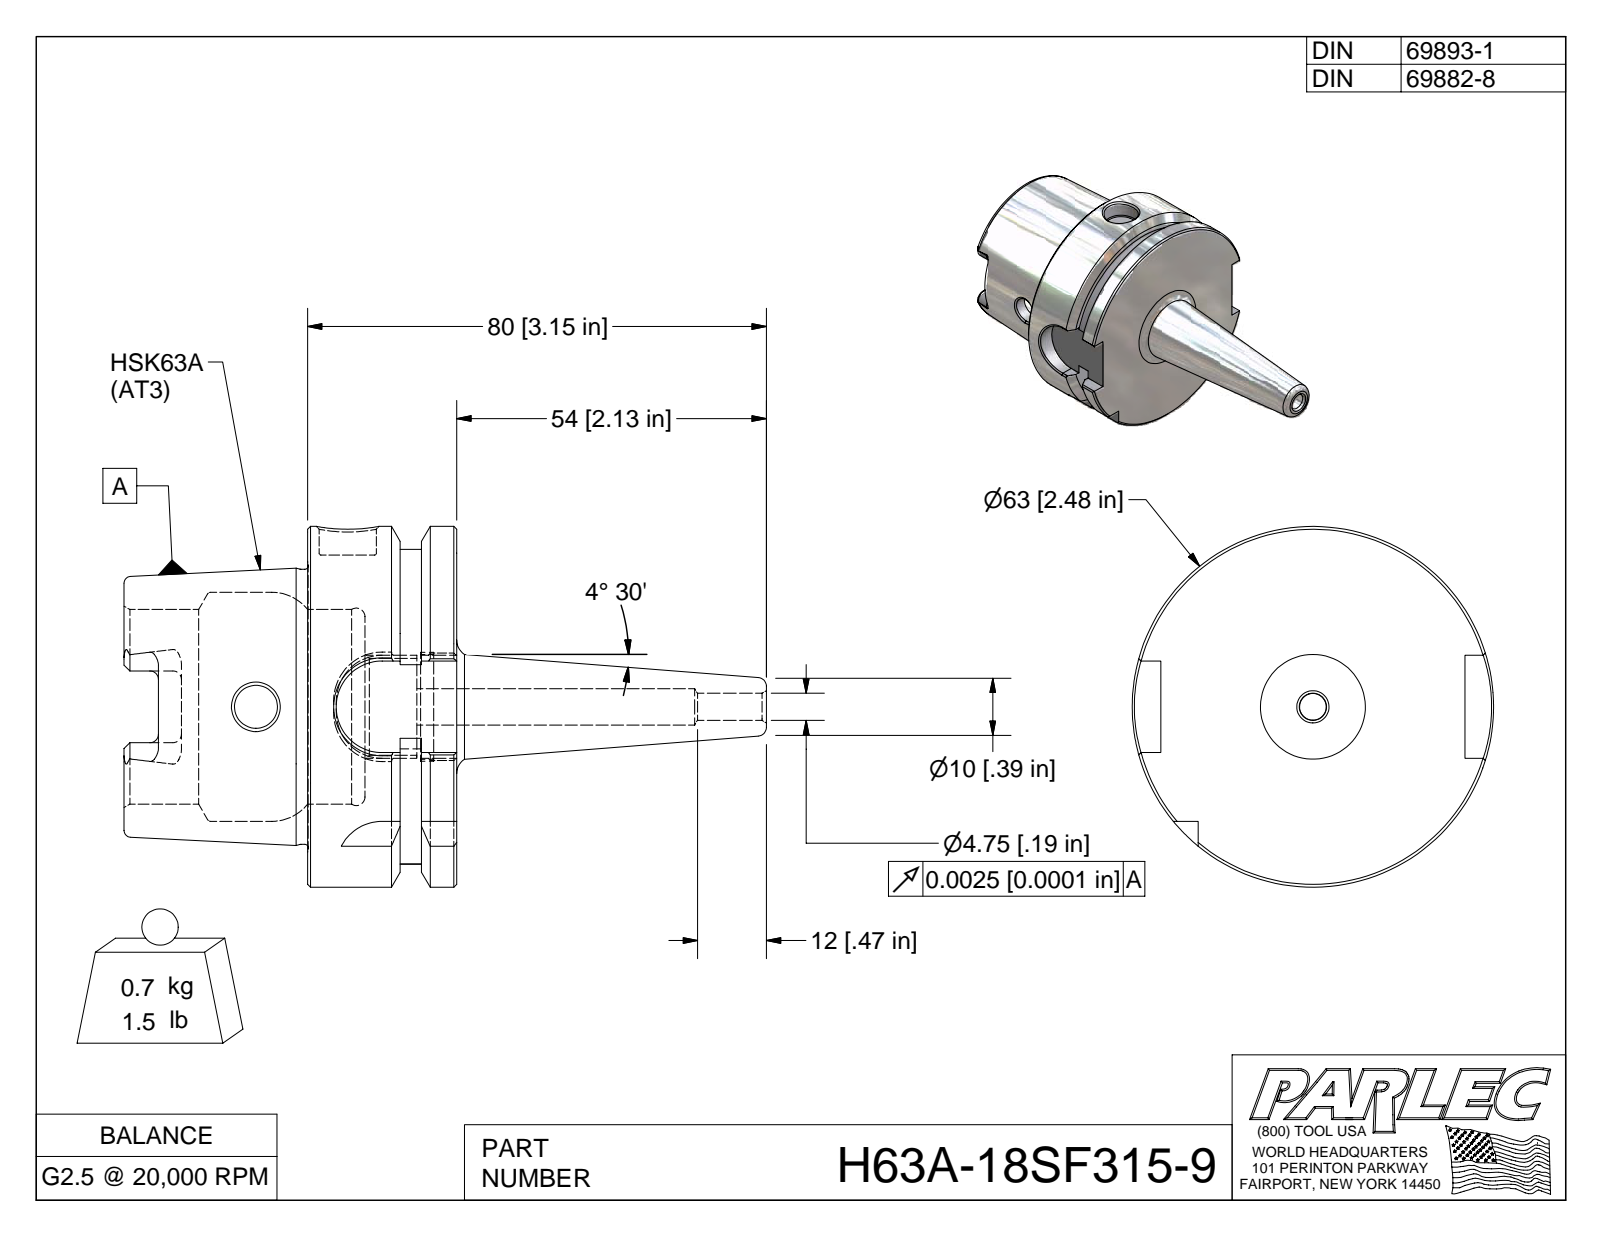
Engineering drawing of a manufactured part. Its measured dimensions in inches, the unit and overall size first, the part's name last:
Units: inches
Overall size (bounding box): 4.409 × 2.48 × 2.48
Round holes (diameter × count): ⌀0.187 ×1, ⌀0.295 ×1, ⌀0.394 ×1, ⌀0.666 ×1, ⌀0.749 ×1, ⌀1.339 ×1, ⌀1.575 ×1
Round bosses / shafts (diameter × count): ⌀2.48 ×1, ⌀1.891 ×1, ⌀0.72 ×1
Partial cylindrical surfaces — rounded edges, fillets, slot ends (radius × count): R0.059 ×6, R0.113 ×4, R0.315 ×4, R1.083 ×1
Main face-to-face distances: 1.024, 0.241, 0.389, 0.394, 0.63, 1.26, 2.283, 1.654, 1.894, 2.043
Volume: 5.442 in³ · Surface area: 40.01 in²
Bodies: 1 solid, 136 faces (49 planar, 33 cylindrical, 54 other)
Part name (STEP PRODUCT): H63A-18SF315-9; H63A-18SF315-9-1
STEP written by: Autodesk Inventor 2009 (AUTOMOTIVE_DESIGN)
